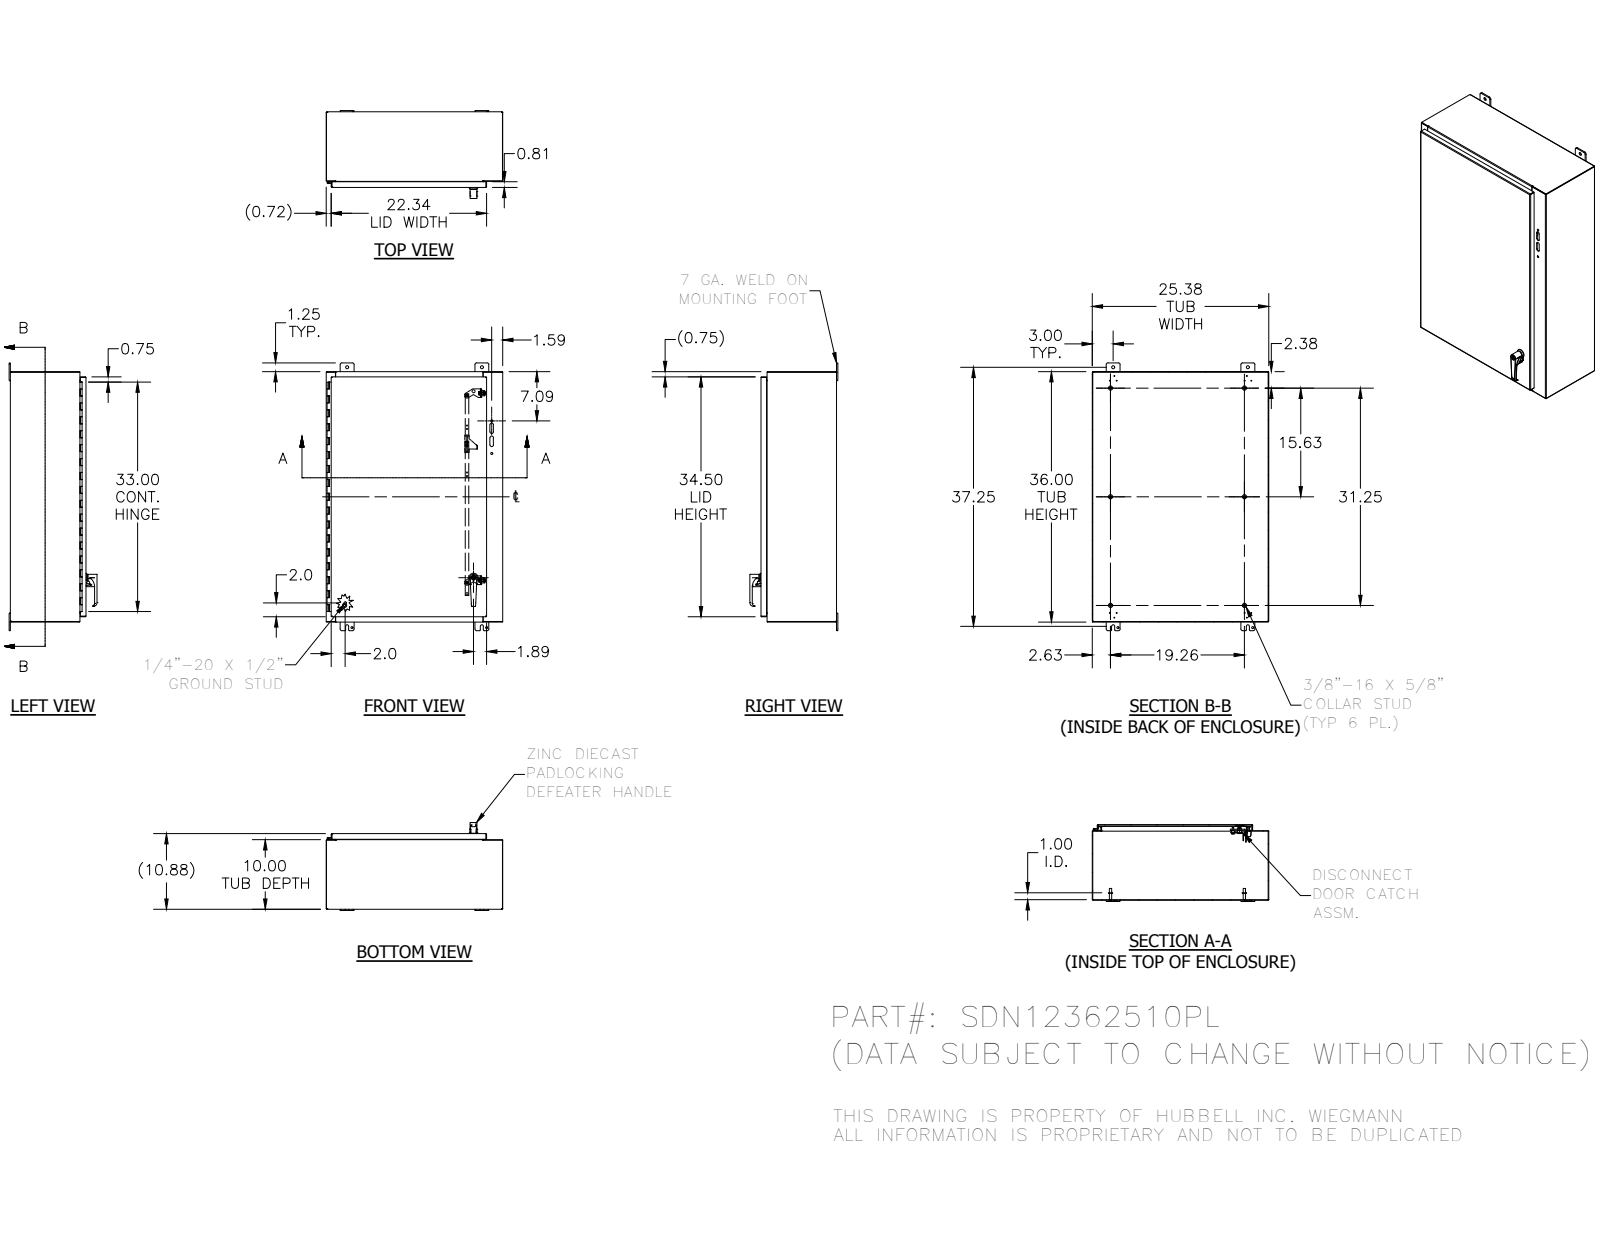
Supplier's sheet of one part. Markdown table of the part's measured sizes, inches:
| quantity | value |
| --- | --- |
| part name | SDN12362510PL; SDN12362510PLBKP; 388116; 34840 (+8 more) |
| STEP written by | Autodesk Inventor 2012 (AUTOMOTIVE_DESIGN) |
| units | inches |
| bodies | 51 solids, 1685 faces (877 planar, 581 cylindrical, 227 other) |
| overall size | 38.5 × 25.38 × 12.649 |
| volume | 257.7 in³ |
| surface area | 6 887 in² |
| round holes (diameter × count) | 0.12 × 12, 0.145 × 6, 0.313 × 4, 0.438 × 4, 0.32 × 3, 0.156 × 2, 0.196 × 2, 0.211 × 2, 0.22 × 2, 0.281 × 2, 0.313 × 2, 0.45 × 2 |
| round bosses / shafts (diameter × count) | 0.625 × 7, 0.33 × 7, 0.437 × 4, 0.3 × 4, 0.25 × 4, 0.225 × 4, 0.19 × 4, 0.75 × 2 |
| partial cylindrical surfaces (radius × count) | 0.02 × 38, 0.012 × 31, 0.25 × 22, 0.031 × 20, 0.105 × 20, 0.025 × 16, 0.125 × 15, 0.07 × 8 |
| main face-to-face distances | 0.074, 10.801, 10.727, 10.875, 25.306, 35.926, 9.926, 0.875, 25.232, 25.38 |
| hole center spacings | 0.759, 1.593, 18.749, 19.38, 26.9, 33.38, 33.394, 34.067 |
